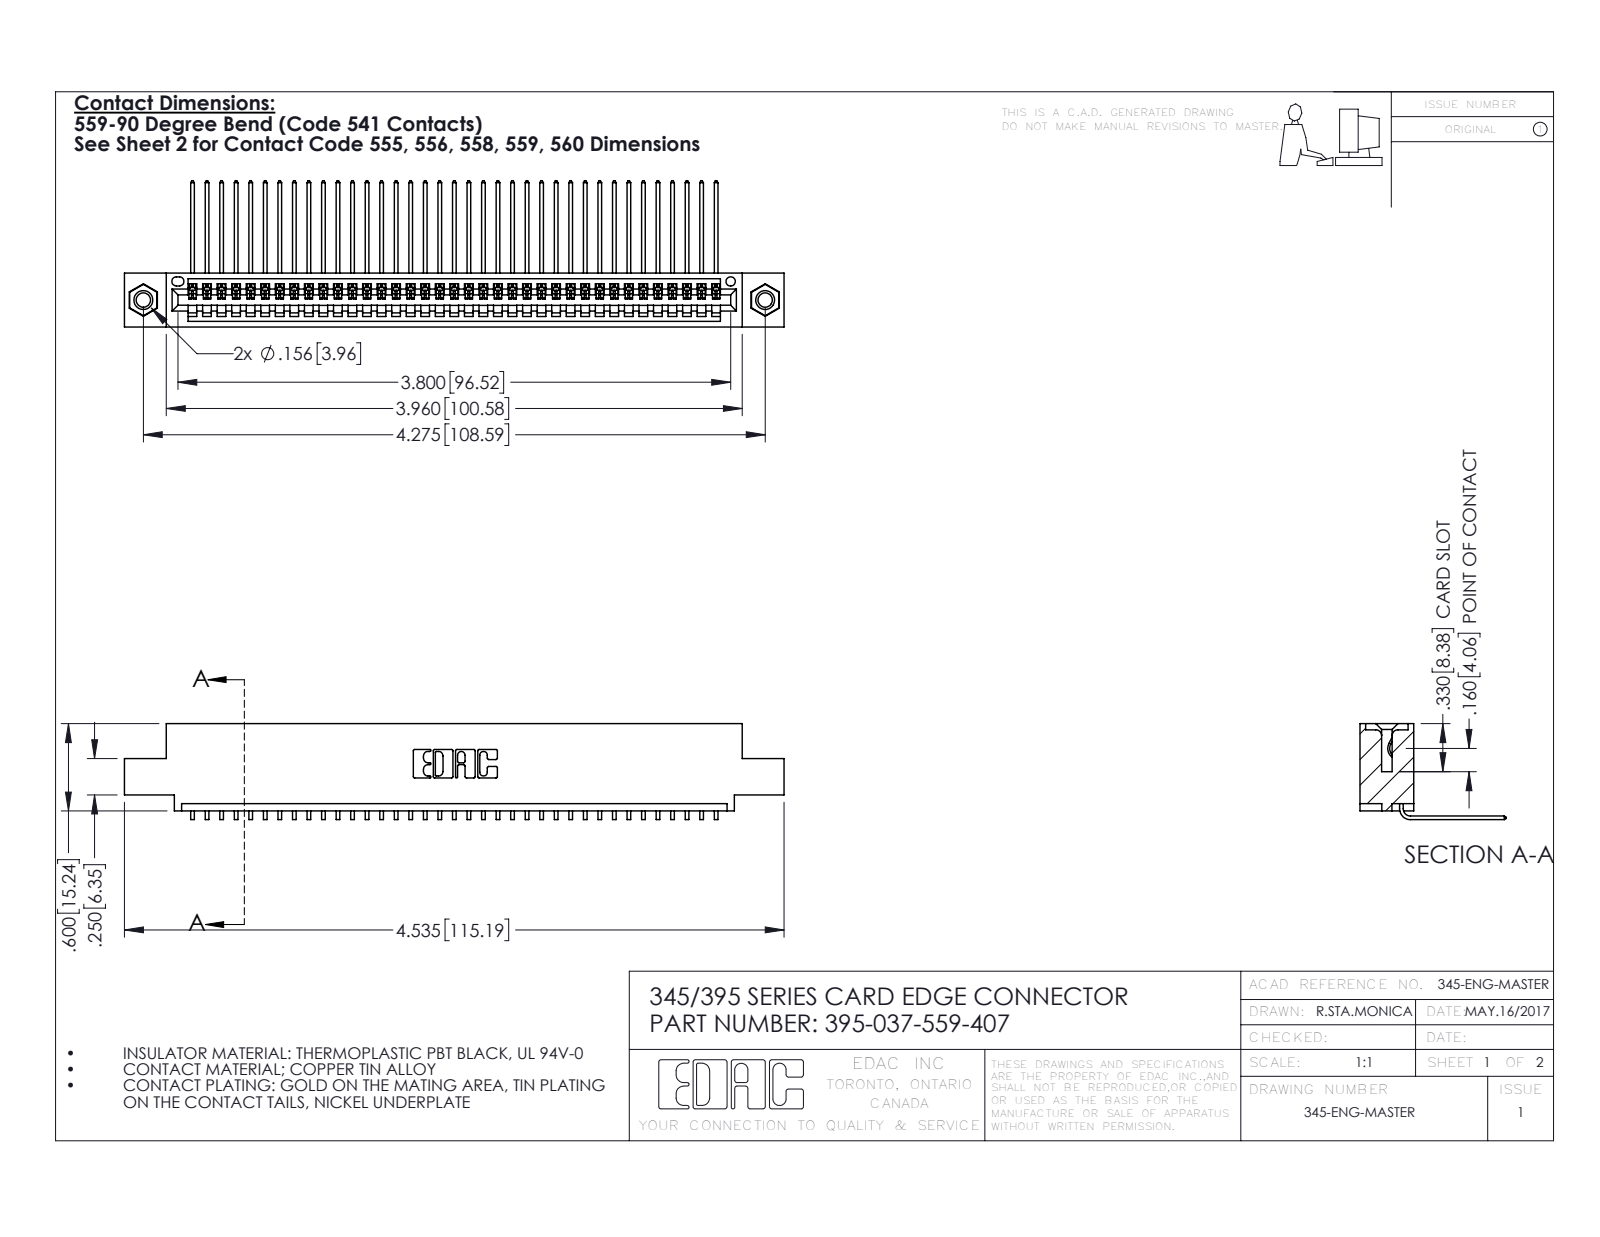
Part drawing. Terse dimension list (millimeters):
name: 345-250-001_345-250-005-103; 395-037-559-407; 345-292-001_558 559 Tail - 1; 345 Part_0.110 Offset - 0.156 Dia-TI
written by: SolidWorks 2016 (CONFIG_CONTROL_DESIGN)
unit: mm
bodies: 40 solids, 2410 faces (1670 planar, 724 cylindrical, 16 other)
size: 115.2 × 25.5 × 16.7
volume: 10 900 mm³; area: 15 300 mm²
holes: 2× ⌀2.5, 2× ⌀3.2, 2× ⌀4, 1× ⌀1.6
bosses: 2× ⌀3.9
rounds: 74× R0.2, 22× R0.3, 6× R0.2, 6× R0.8, 3× R0.7, 2× R0.8, 2× R1, 1× R0.4
face distances: 1.8, 7.6, 9.4, 5.1, 2.5, 6.9, 0.6, 5.7, 3.8, 1.8
hole spacings: 6.9, 102.6, 108.6
